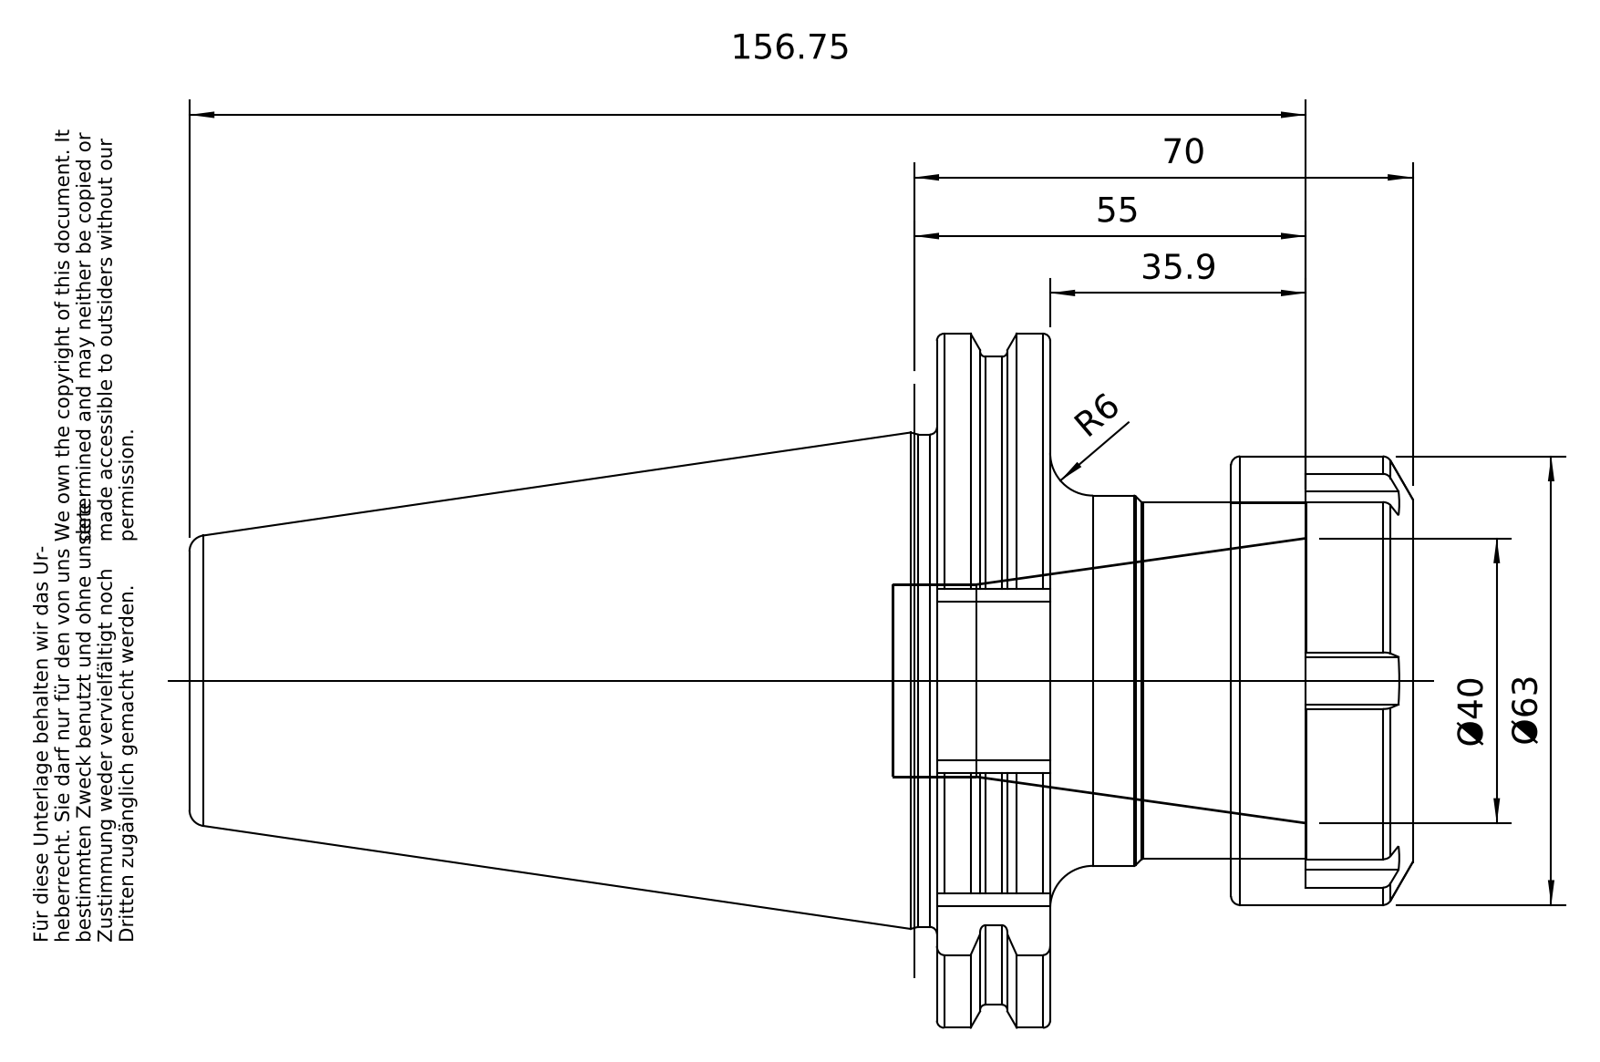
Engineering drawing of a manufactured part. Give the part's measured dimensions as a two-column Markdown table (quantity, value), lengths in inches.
| quantity | value |
| --- | --- |
| part name | 50-320-40; 83-912-40; 50-320-40_ASM |
| STEP written by | PRO/ENGINEER BY PARAMETRIC TECHNOLOGY CORPORATION, 2010430 (CONFIG_CONTROL_DESIGN) |
| units | inches |
| bodies | 2 solids, 149 faces (49 planar, 38 cylindrical, 62 other) |
| overall size | 6.756 × 3.837 × 3.701 |
| volume | 26.92 in³ |
| surface area | 99.17 in² |
| round holes (diameter × count) | 0.817 × 1, 0.985 × 1, 1.012 × 1, 1.063 × 1 |
| round bosses / shafts (diameter × count) | 3.583 × 1, 2.722 × 1, 2.48 × 1, 2.047 × 1, 1.969 × 1, 0.945 × 1 |
| partial cylindrical surfaces (radius × count) | 0.106 × 6, 0.069 × 5, 1.919 × 1 |
| main face-to-face distances | 1.002, 0.624, 1.626, 2.63, 2.006, 1.004, 2.039, 1.415, 0.413, 0.591 |
